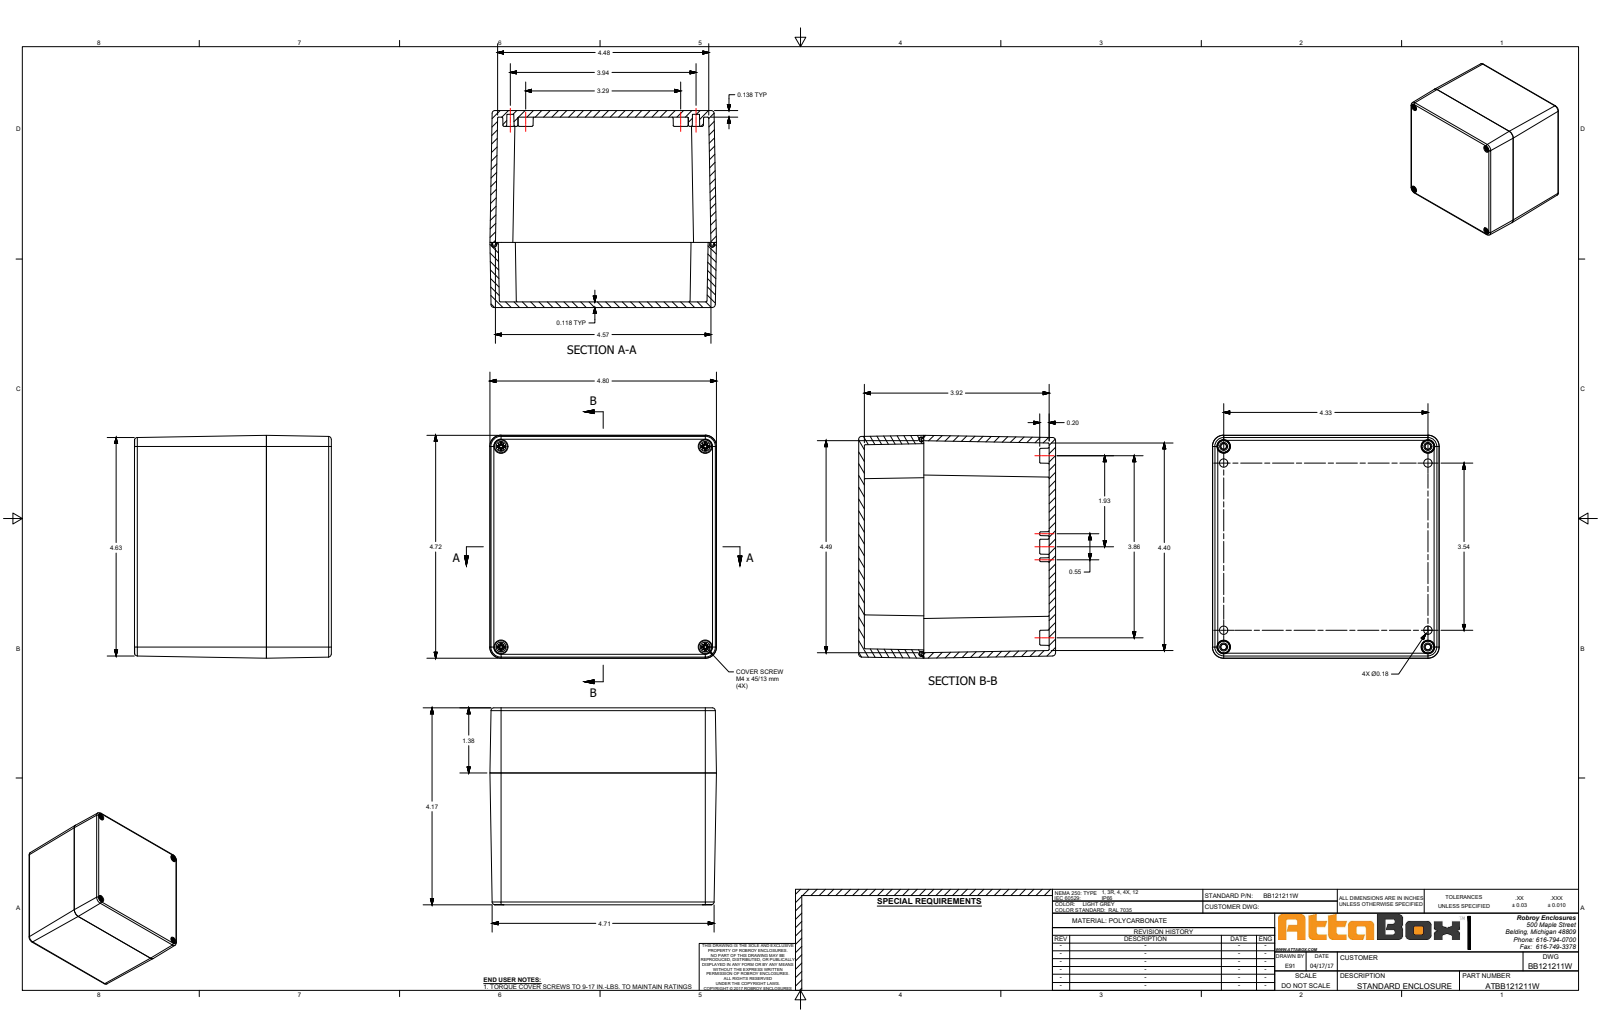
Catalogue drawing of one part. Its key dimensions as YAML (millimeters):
part_name: "BB121211W"
step_written_by: "SolidWorks 2018 (AUTOMOTIVE_DESIGN)"
units: millimeters
bodies: {solids: 11, faces: 1669, planar: 611, cylindrical: 440, other: 618}
overall_size: [122, 120, 106]
volume: 279900
surface_area: 183000
round_holes:
  - {diameter: 4.5, count: 8}
  - {diameter: 3.3, count: 4}
  - {diameter: 4.8, count: 4}
  - {diameter: 5.1, count: 4}
  - {diameter: 7, count: 4}
  - {diameter: 7.3, count: 4}
  - {diameter: 7.5, count: 4}
round_bosses_or_shafts:
  - {diameter: 6.8, count: 4}
  - {diameter: 4.4, count: 4}
  - {diameter: 4, count: 4}
  - {diameter: 3.3, count: 4}
partial_cylinders:
  - {radius: 1, count: 48}
  - {radius: 0.5, count: 40}
  - {radius: 5, count: 12}
  - {radius: 1.5, count: 8}
  - {radius: 2.5, count: 8}
  - {radius: 2.6, count: 4}
  - {radius: 3.1, count: 4}
  - {radius: 3.3, count: 4}
face_to_face_distances: [2.9, 106, 3.5, 103, 3, 99.5, 102.5, 4.5, 120, 117]
hole_center_spacings: [9, 99, 110, 110.4, 148, 90, 108, 142.1]
